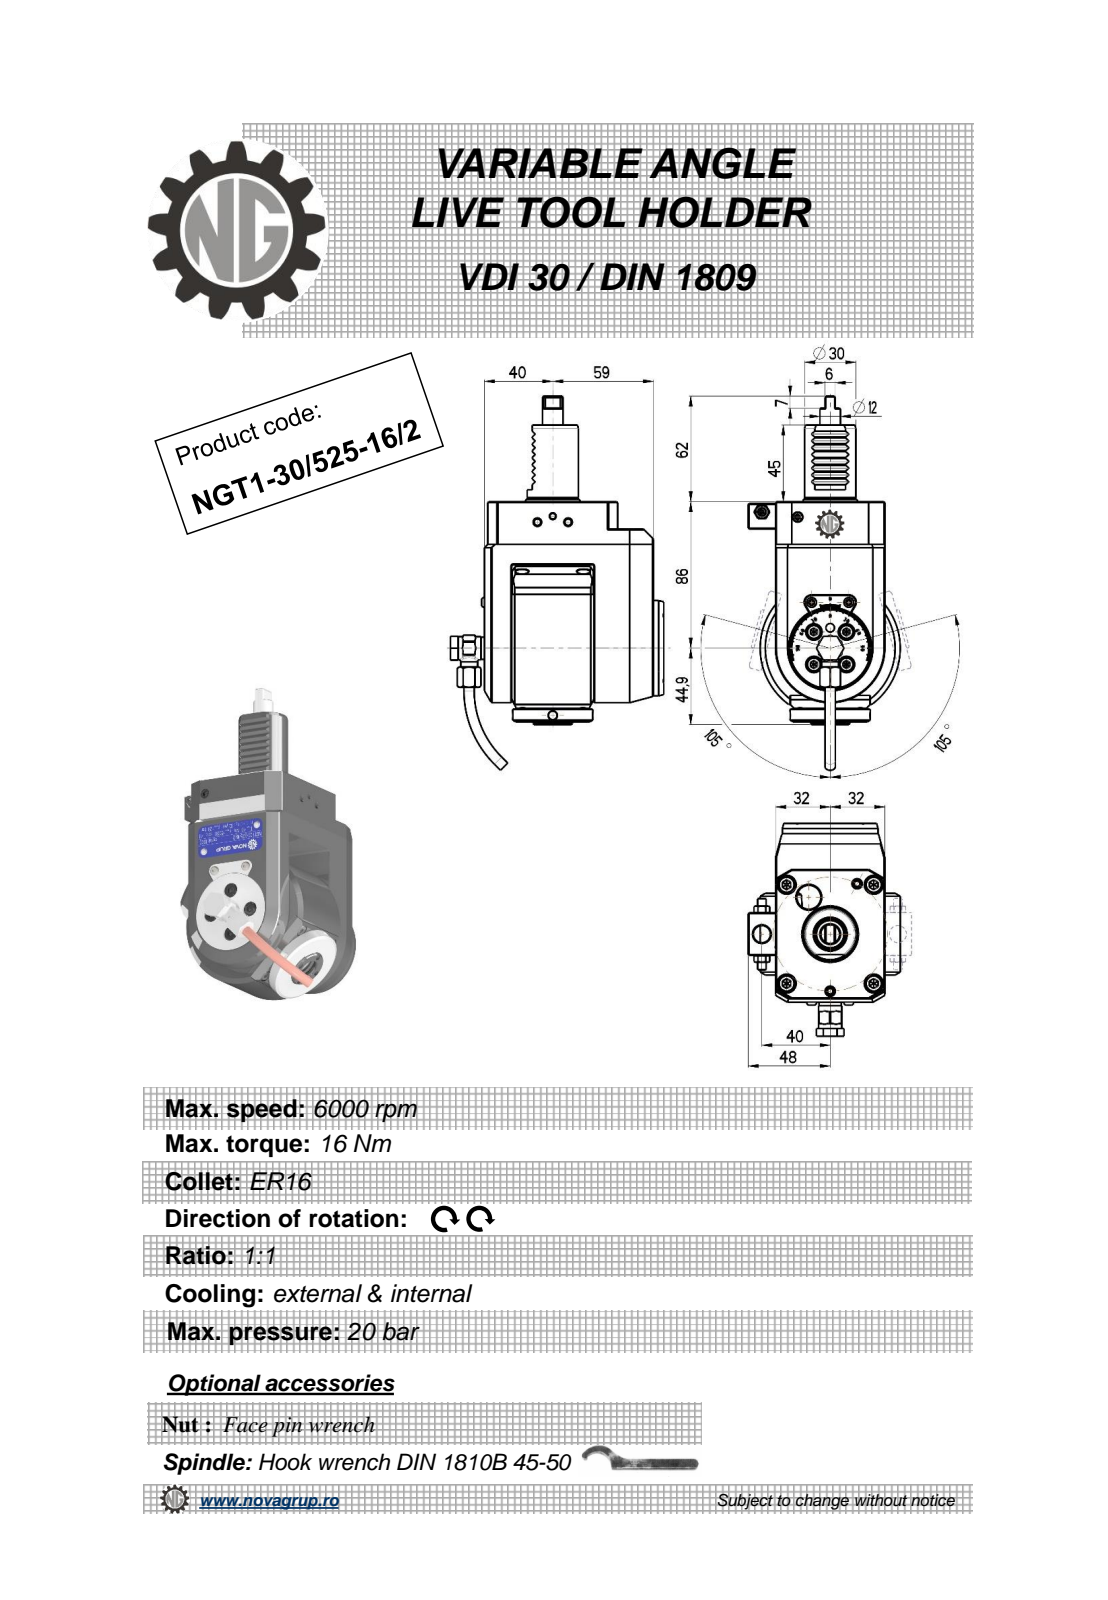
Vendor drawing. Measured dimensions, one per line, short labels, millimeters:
name: NGT1_30_521_16_2
written by: PRO/ENGINEER BY PARAMETRIC TECHNOLOGY CORPORATION, 2010280 (CONFIG_CONTROL_DESIGN)
unit: mm
bodies: 1 solid, 489 faces (208 planar, 134 cylindrical, 147 other)
size: 219.67 × 124.9 × 89
volume: 770 185 mm³; area: 70 510 mm²
holes: 4× ⌀3.2, 3× ⌀4, 2× ⌀5, 2× ⌀10, 1× ⌀3, 1× ⌀4.2, 1× ⌀6.2, 1× ⌀9, 1× ⌀9.5, 1× ⌀11, 1× ⌀12.5
bosses: 2× ⌀6, 2× ⌀5.7, 1× ⌀56, 1× ⌀47, 1× ⌀35, 1× ⌀30, 1× ⌀23, 1× ⌀13.6
rounds: 12× R0.26, 8× R0.3, 6× R0.16, 6× R0.5, 2× R1, 1× R7.7, 1× R32, 1× R41
face distances: 64, 16, 37, 99, 6, 105, 21, 14, 62, 35
hole spacings: 9.25, 13.08, 18.5, 41.06, 49.87, 50.26, 0.4, 30.75
